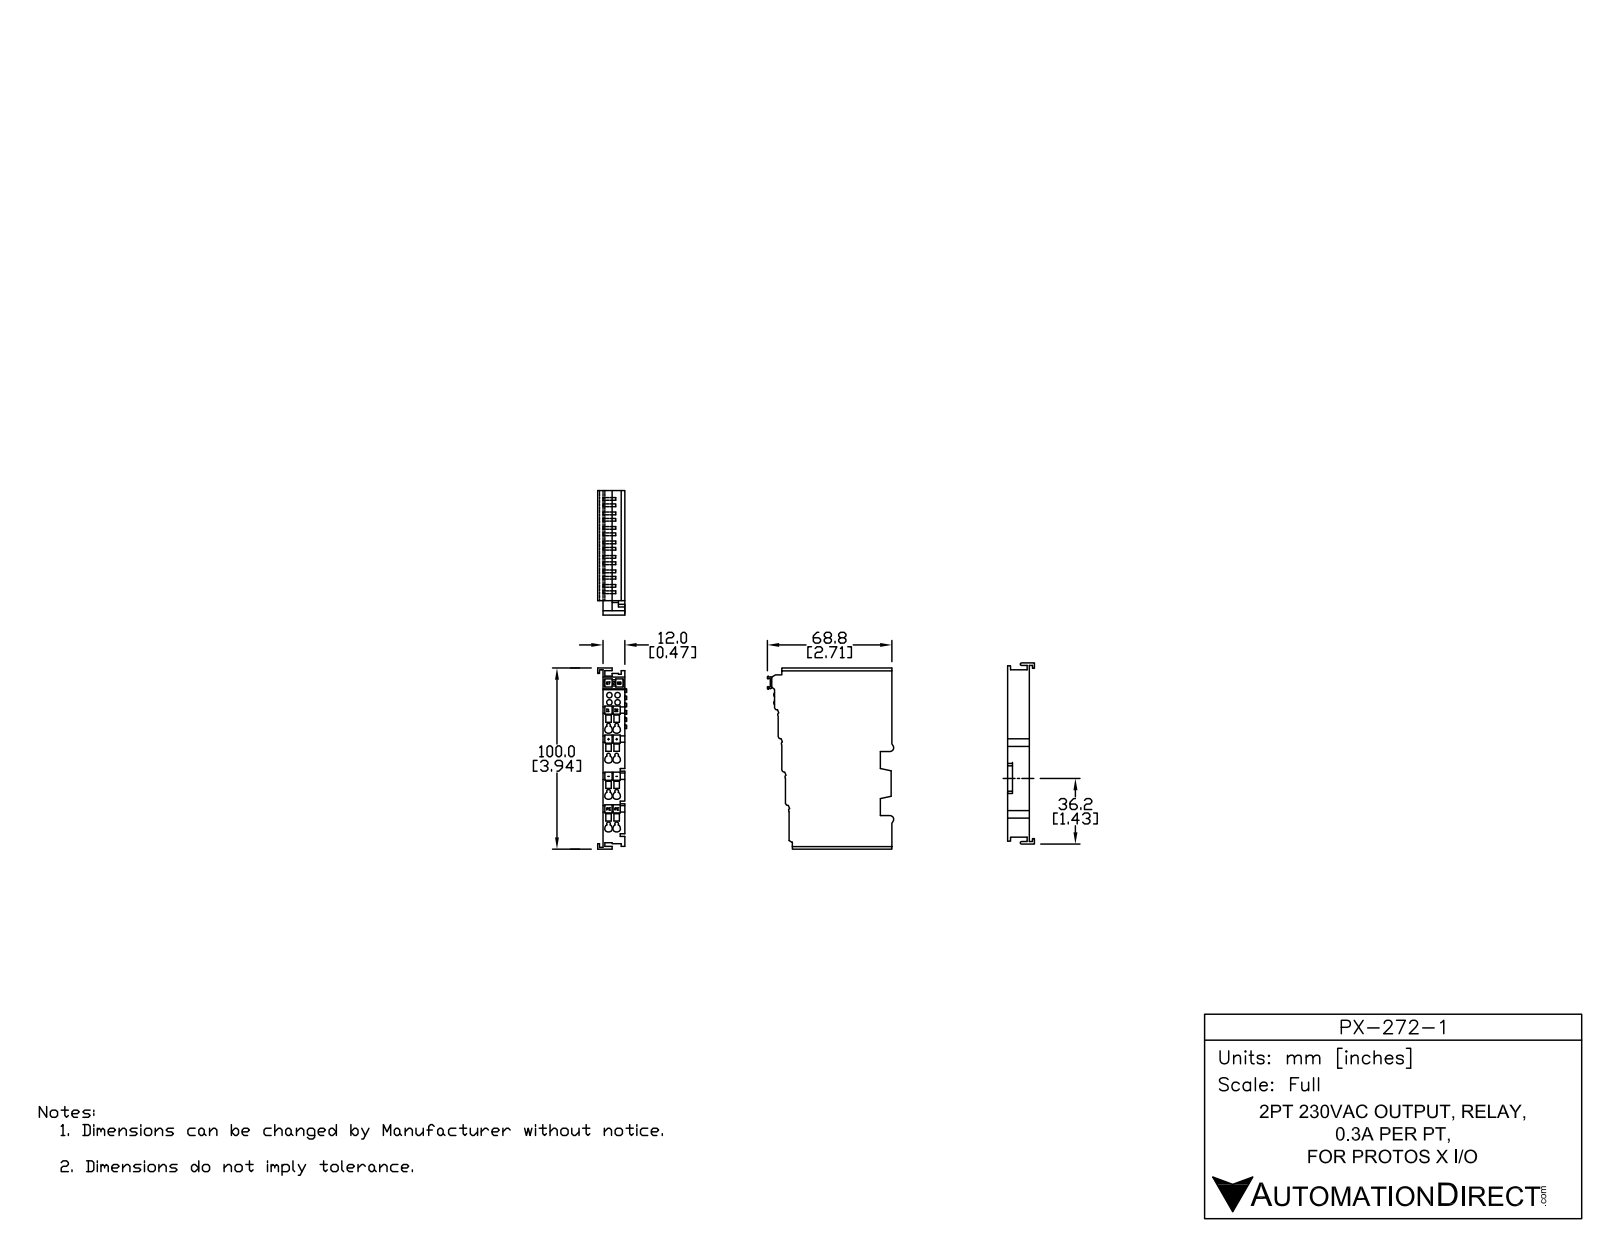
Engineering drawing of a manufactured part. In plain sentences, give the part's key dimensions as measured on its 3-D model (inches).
The part is named "PX-272". Its 3-D file was written by "SolidWorks 2014 (AUTOMOTIVE_DESIGN)". It is 28 solids with 1367 faces: 963 planar, 344 cylindrical and 60 other. Overall it measures 3.947 by 2.806 by 0.596 inches. Its volume is 3.564 cubic inches and its surface area 52.52 square inches. Round holes: 8 of diameter 0.157, 4 of diameter 0.138. Partial cylindrical surfaces (rounded edges, fillets, slot ends): 46 of radius 0.012, 35 of radius 0.01, 12 of radius 0.015, 10 of radius 0.005, 9 of radius 0.039, 8 of radius 0.016, 4 of radius 0.007, 4 of radius 0.041. The main face-to-face distances are 0.472, 0.039, 0.079, 0.394, 0.073, 0.433, 0.343, 0.157, 0.124, 0.048. The hole center spacings are 0.177, 0.197, 0.724, 0.751, 0.25, 0.63, 0.66, 0.804.
